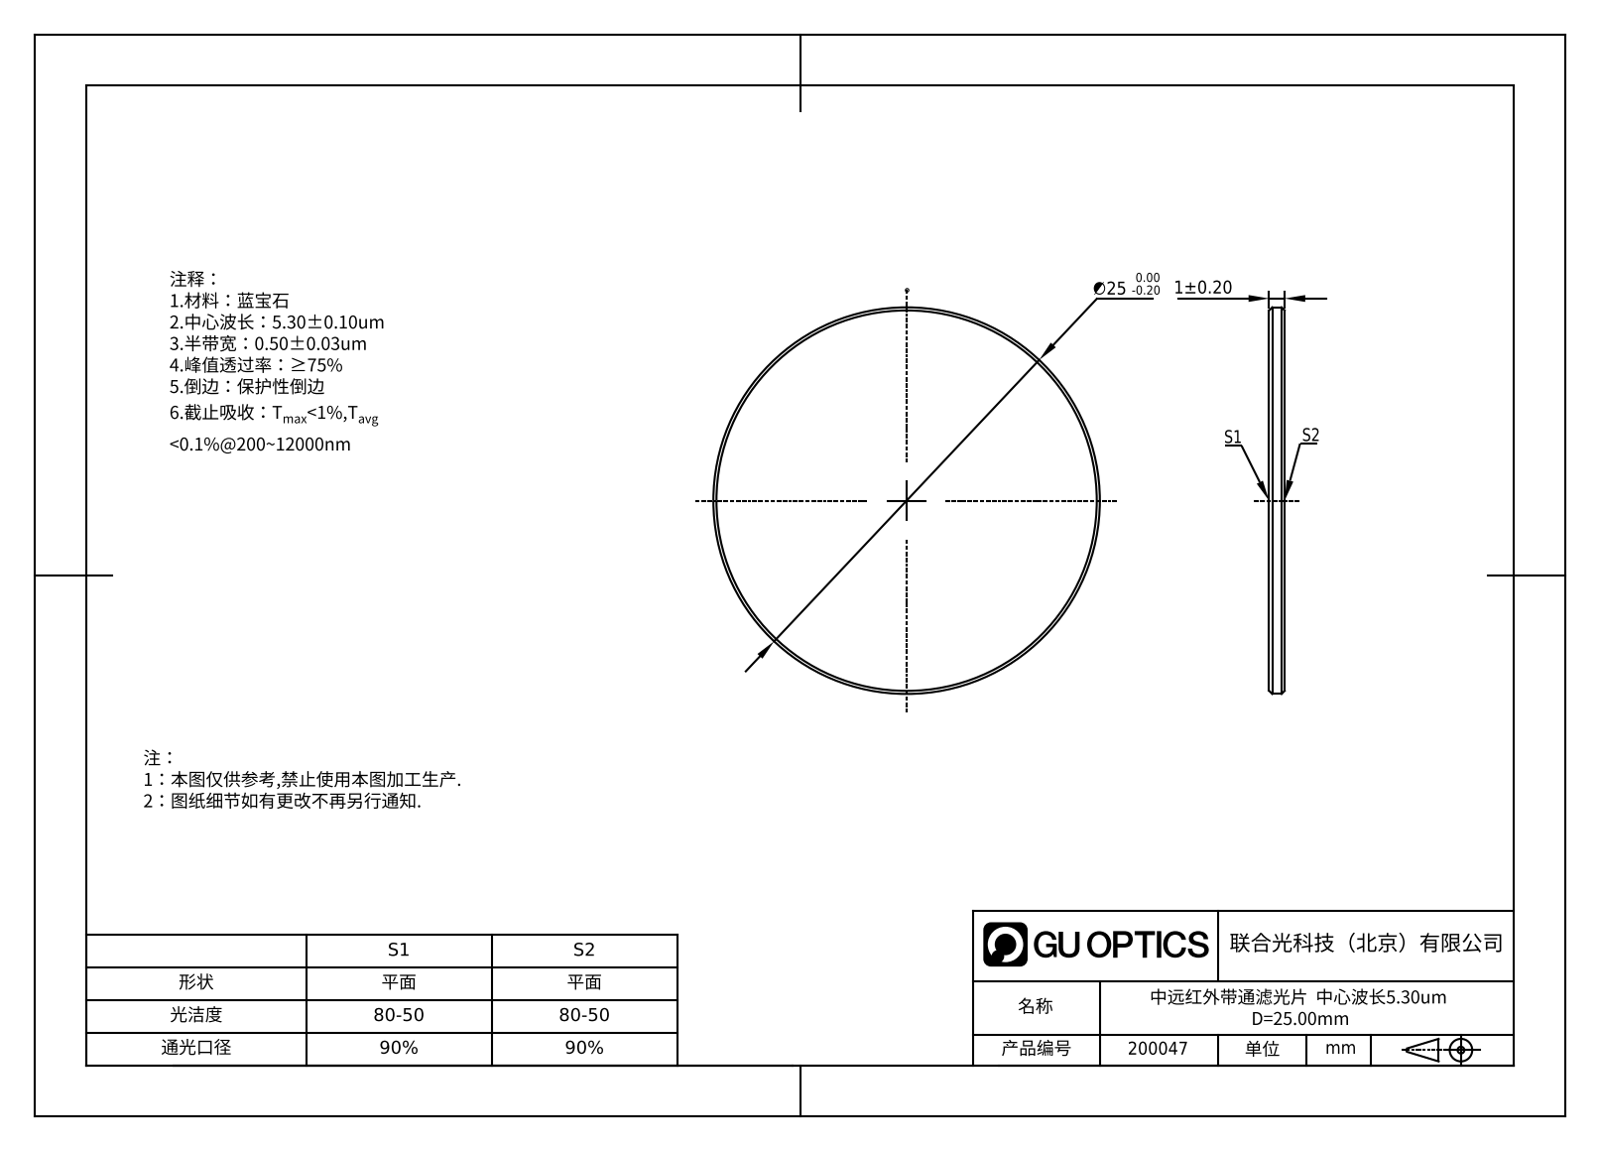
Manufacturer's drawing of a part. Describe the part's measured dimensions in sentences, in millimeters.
The part is named "GNIF-050-5300-D25". Its 3-D file was written by "SolidWorks 2022 (AUTOMOTIVE_DESIGN)". It is 1 solid with 8 faces: 2 planar, 2 cylindrical and 4 other. Overall it measures 25 by 25 by 1 millimeters. Its volume is 488 cubic millimeters and its surface area 1 042 square millimeters. Round bosses or shafts: 1 of diameter 25. The main face-to-face distances are 1.
